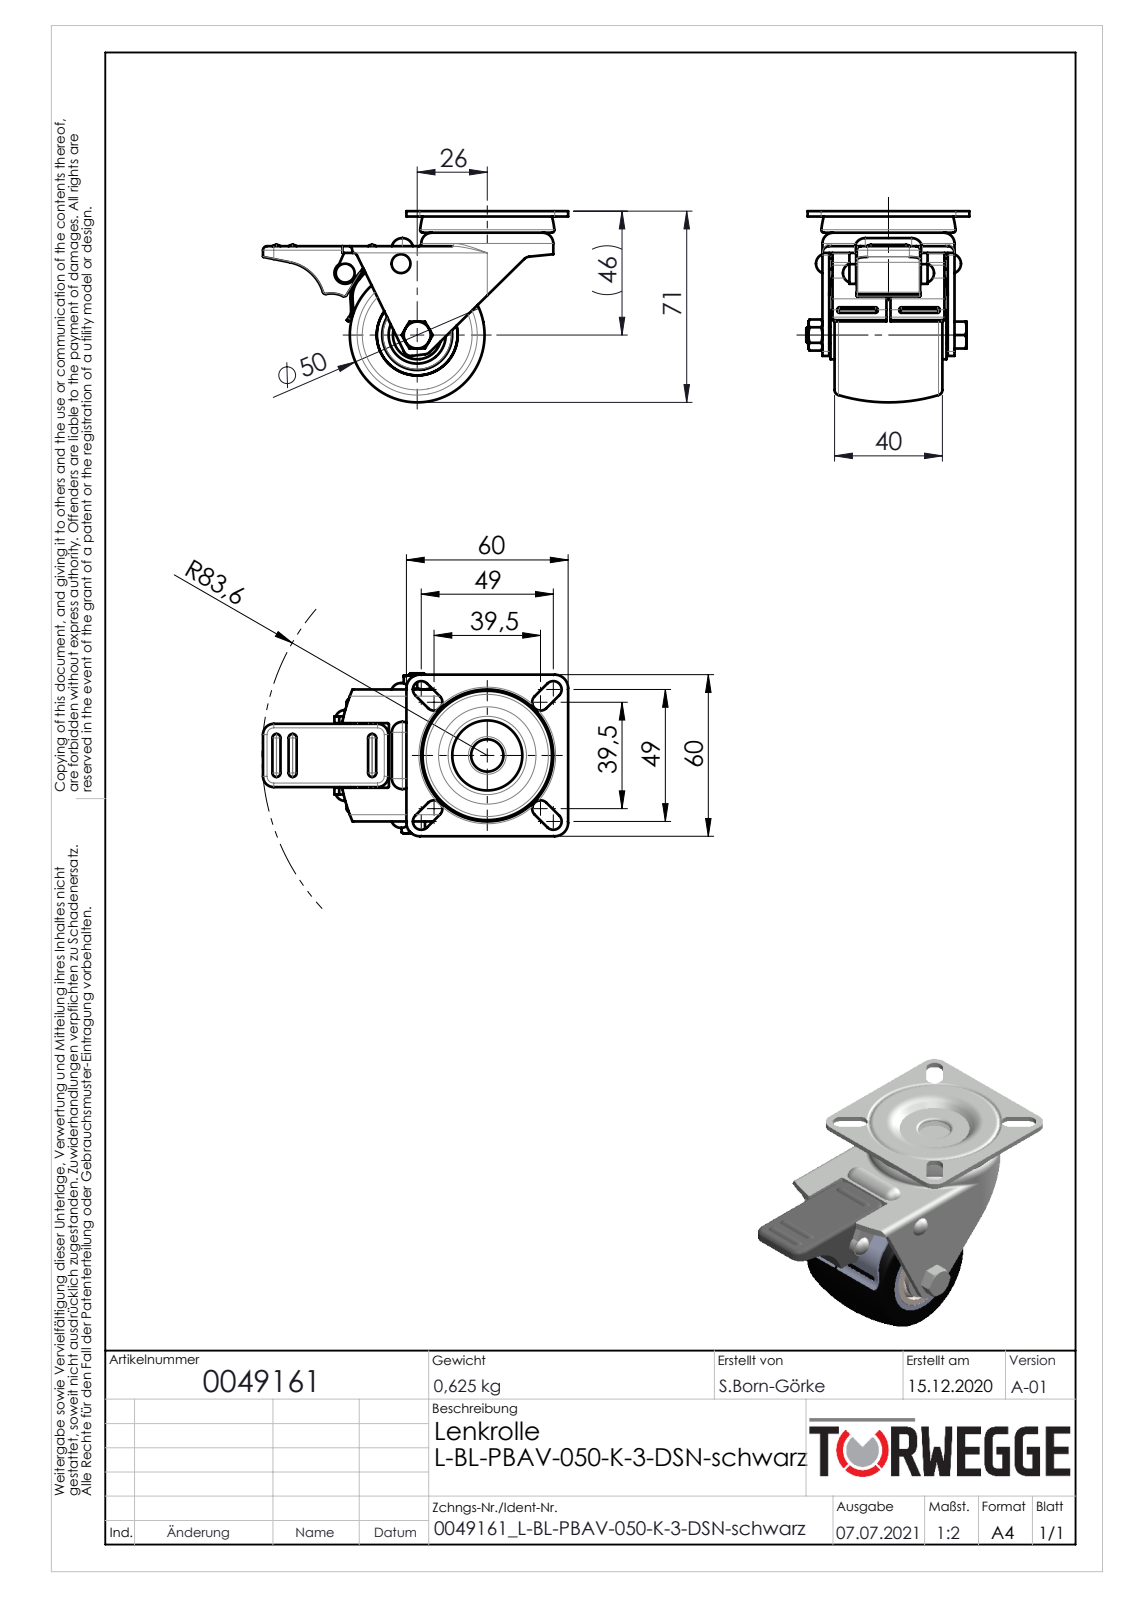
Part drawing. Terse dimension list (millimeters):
name: 0049161
written by: SolidWorks 2020 (AUTOMOTIVE_DESIGN)
unit: mm
bodies: 18 solids, 562 faces (152 planar, 183 cylindrical, 227 other)
size: 113.22 × 71 × 60.5
volume: 110 900 mm³; area: 62 453 mm²
holes: 2× ⌀4, 1× ⌀2.5, 1× ⌀5, 1× ⌀6, 1× ⌀6.1, 1× ⌀8, 1× ⌀10, 1× ⌀12, 1× ⌀14.5, 1× ⌀20, 1× ⌀21.2, 1× ⌀26
bosses: 1× ⌀21.5, 1× ⌀18, 1× ⌀14.8, 1× ⌀9.95, 1× ⌀7.9
rounds: 8× R0.2, 8× R0.75, 8× R3.1, 8× R4, 6× R2.4, 6× R5, 5× R1.5, 4× R0.5
face distances: 2.5, 2, 8, 5, 4.5, 46.5, 44.5, 42, 7.5, 32
hole spacings: 21.01, 27.17, 35.26
